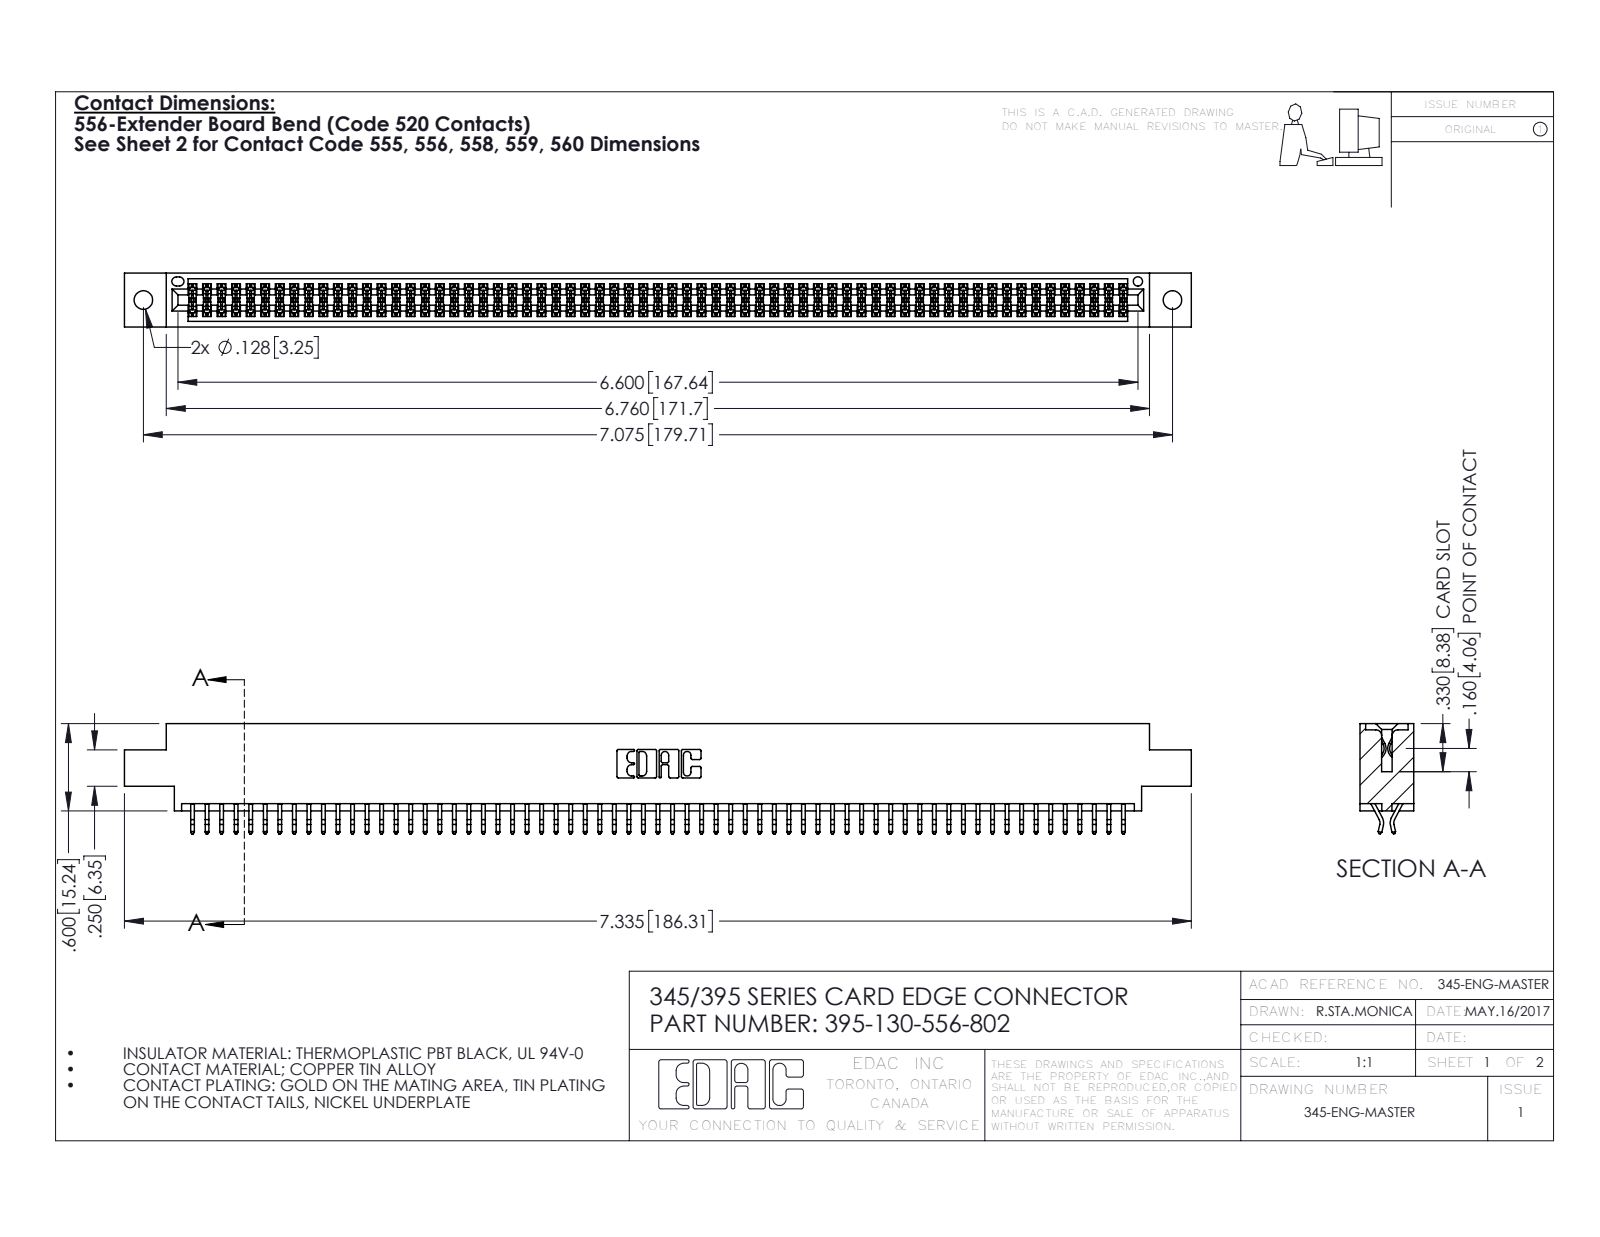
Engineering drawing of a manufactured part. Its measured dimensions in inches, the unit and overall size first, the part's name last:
Units: inches
Overall size (bounding box): 7.335 × 0.757 × 0.37
Round holes (diameter × count): ⌀0.128 ×2, ⌀0.064 ×1
Partial cylindrical surfaces — rounded edges, fillets, slot ends (radius × count): R0.006 ×195, R0.01 ×22, R0.007 ×6, R0.031 ×6, R0.026 ×3, R0.01 ×2, R0.014 ×2, R0.019 ×2
Main face-to-face distances: 0.298, 0.072, 0.37, 0.2, 0.025, 0.098, 0.272, 0.225, 0.175, 0.149
Hole centre spacings: 0.27, 6.839, 7.075
Volume: 1.108 in³ · Surface area: 41.91 in²
Bodies: 131 solids, 7410 faces (4894 planar, 2516 cylindrical, 0 other)
Part name (STEP PRODUCT): 345 Part_0.170 Offset - 0.128 Dia; 395-130-556-802; 345-292-001_556 Tail
STEP written by: SolidWorks 2016 (CONFIG_CONTROL_DESIGN)
